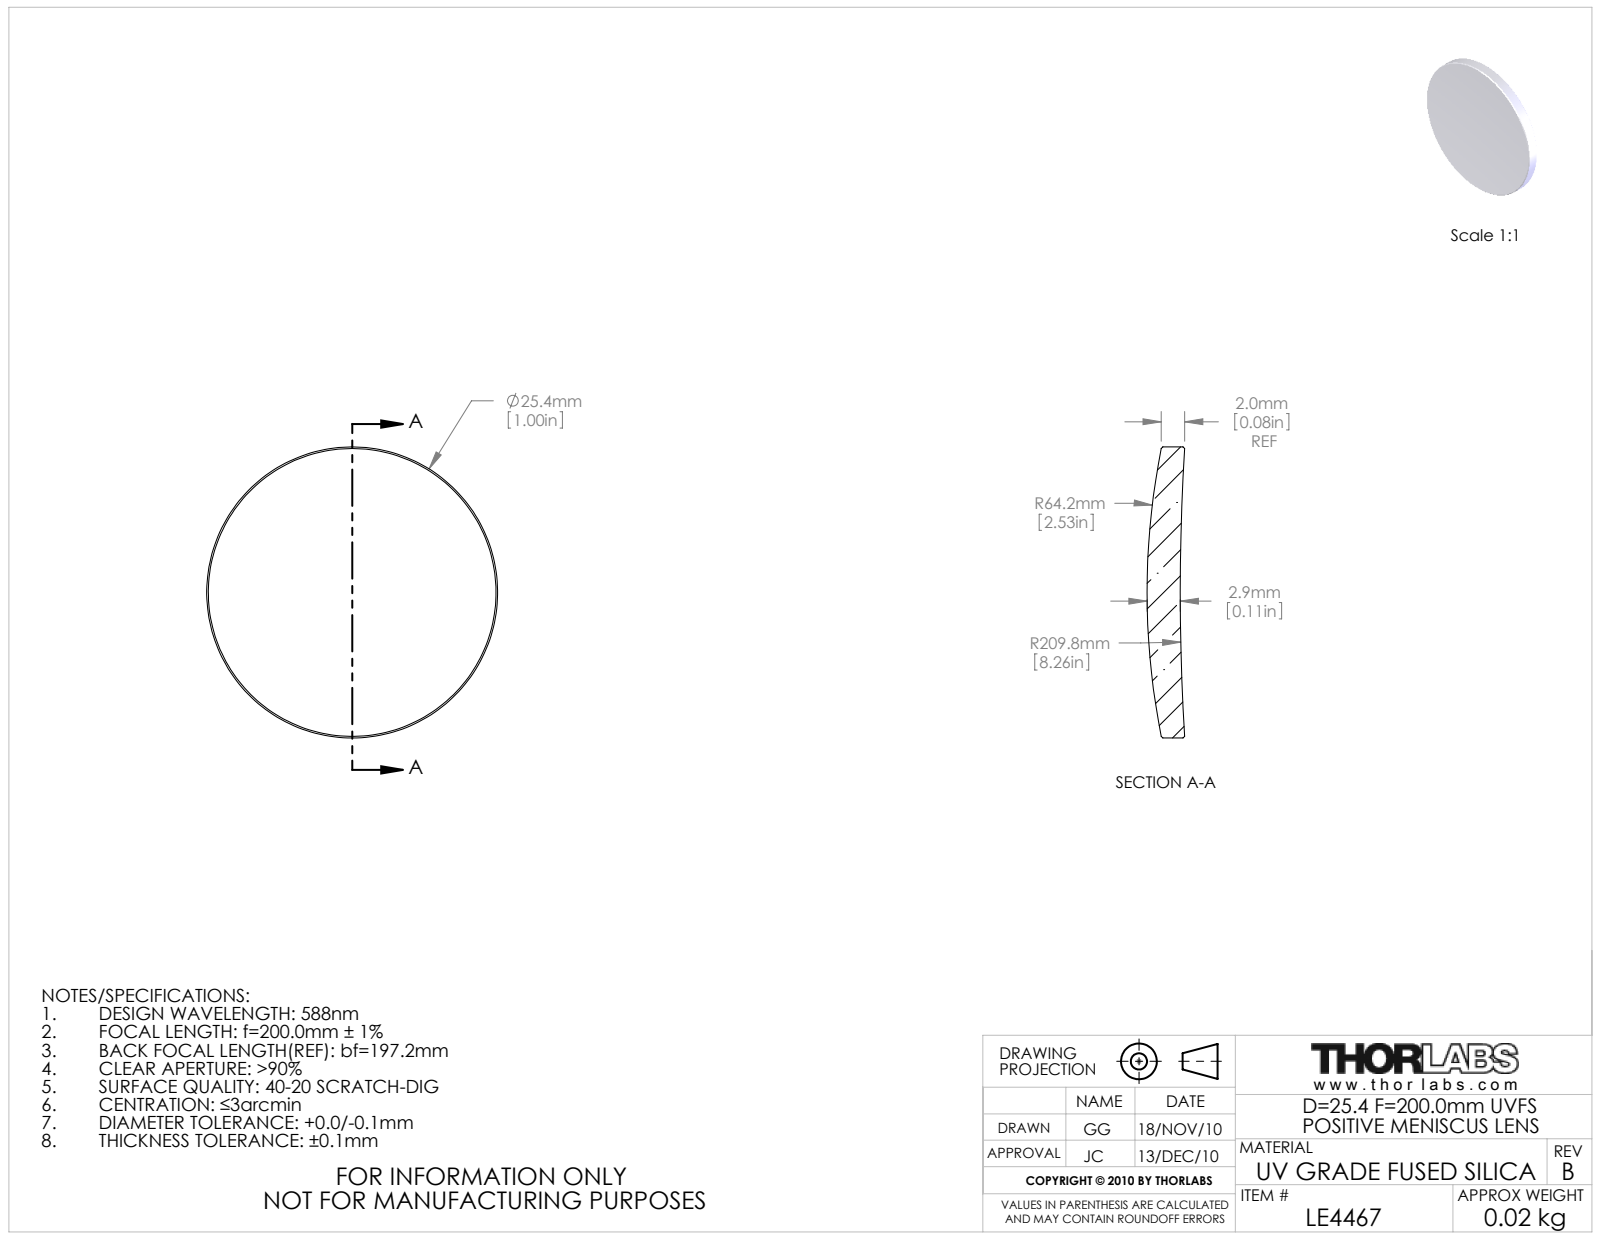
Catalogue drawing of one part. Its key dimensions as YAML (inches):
part_name: "4207-E0W"
step_written_by: "SolidWorks 2009 (AUTOMOTIVE_DESIGN)"
units: inches
bodies: {solids: 1, faces: 10, planar: 0, cylindrical: 2, other: 8}
overall_size: [1, 1, 0.129]
volume: 0.076
surface_area: 1.81
round_bosses_or_shafts:
  - {diameter: 1, count: 1}
